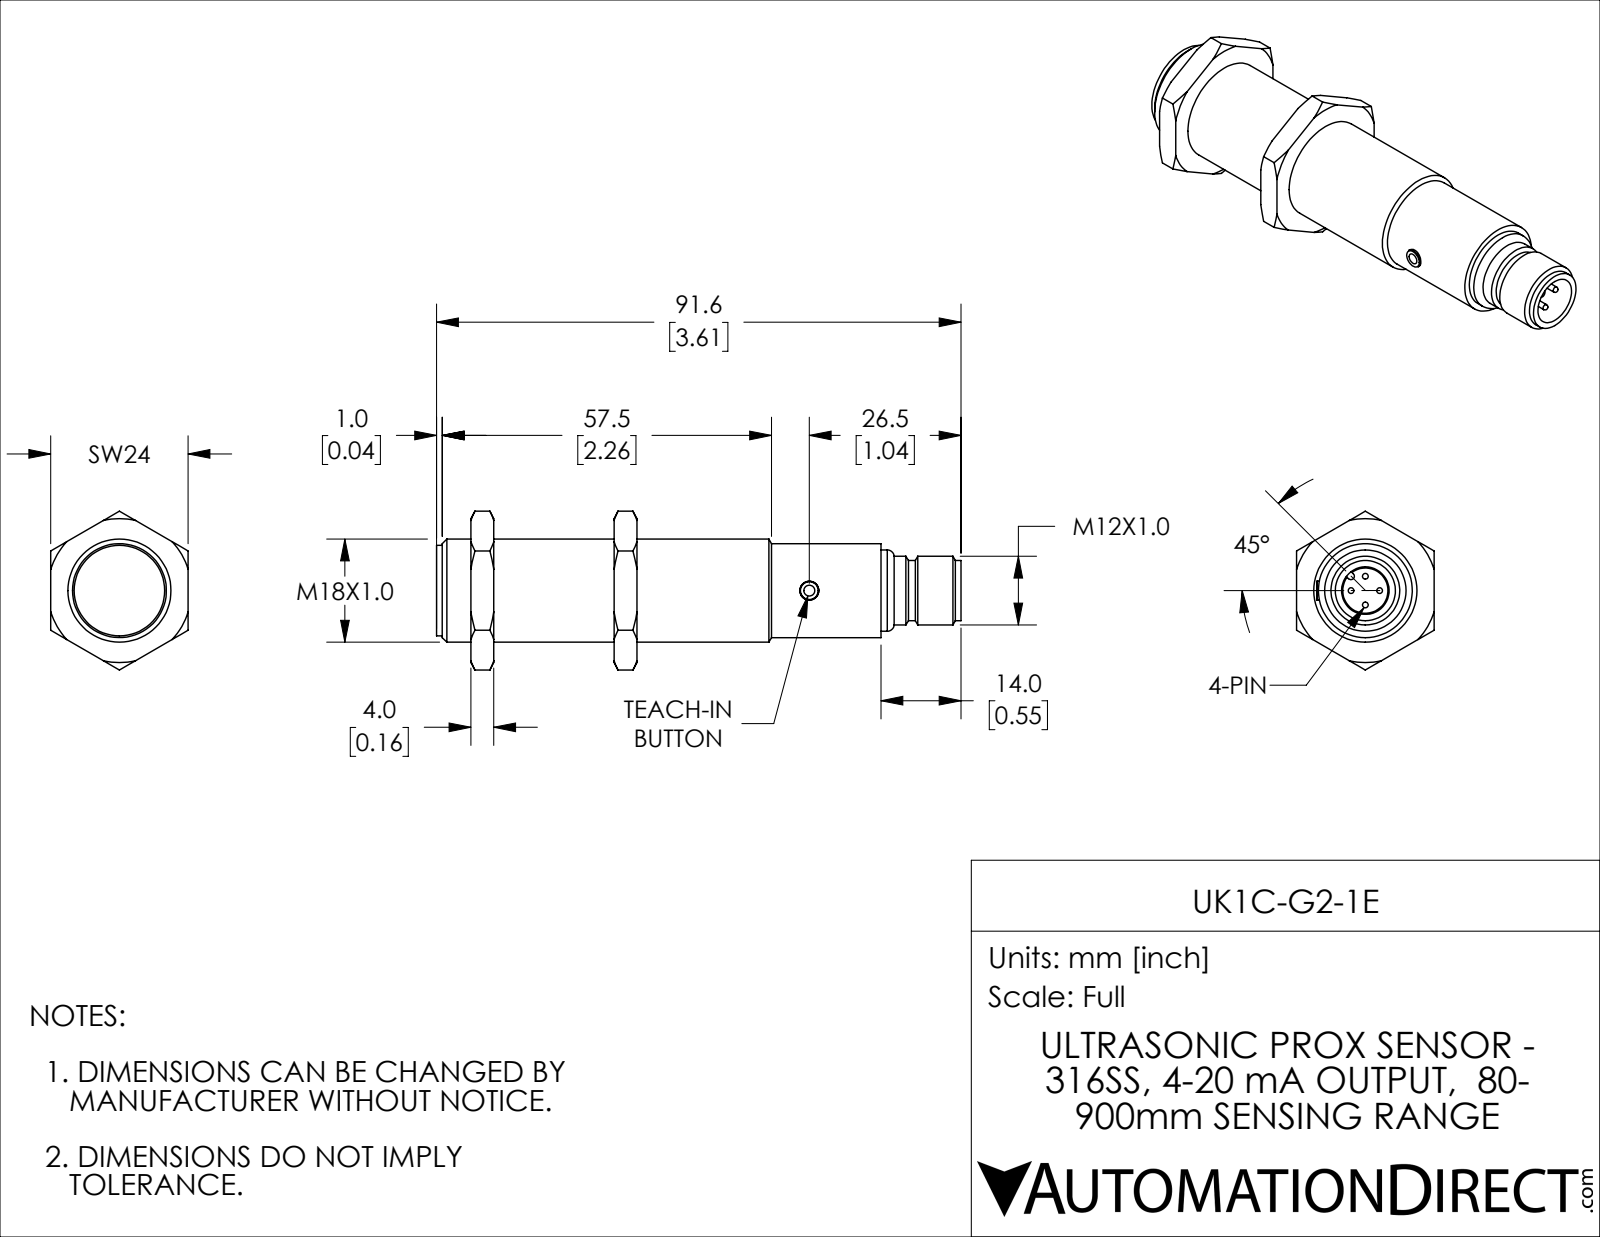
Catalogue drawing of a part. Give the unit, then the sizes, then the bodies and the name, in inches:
Units: inches
Overall size (bounding box): 3.606 × 1.091 × 0.945
Round holes (diameter × count): ⌀0.13 ×1, ⌀0.327 ×1, ⌀0.709 ×1
Round bosses / shafts (diameter × count): ⌀0.039 ×4, ⌀0.646 ×1, ⌀0.622 ×1, ⌀0.559 ×1, ⌀0.472 ×1, ⌀0.413 ×1
Partial cylindrical surfaces — rounded edges, fillets, slot ends (radius × count): R0.024 ×1
Main face-to-face distances: 0.984, 0.157, 0.945, 1.142, 0.827, 0.236, 0.394, 1.22, 1.378, 3.055
Volume: 1.338 in³ · Surface area: 11.97 in²
Bodies: 4 solids, 113 faces (27 planar, 35 cylindrical, 51 other)
Part name (STEP PRODUCT): UK1C-G2-1E
STEP written by: SolidWorks 2018 (AUTOMOTIVE_DESIGN)
